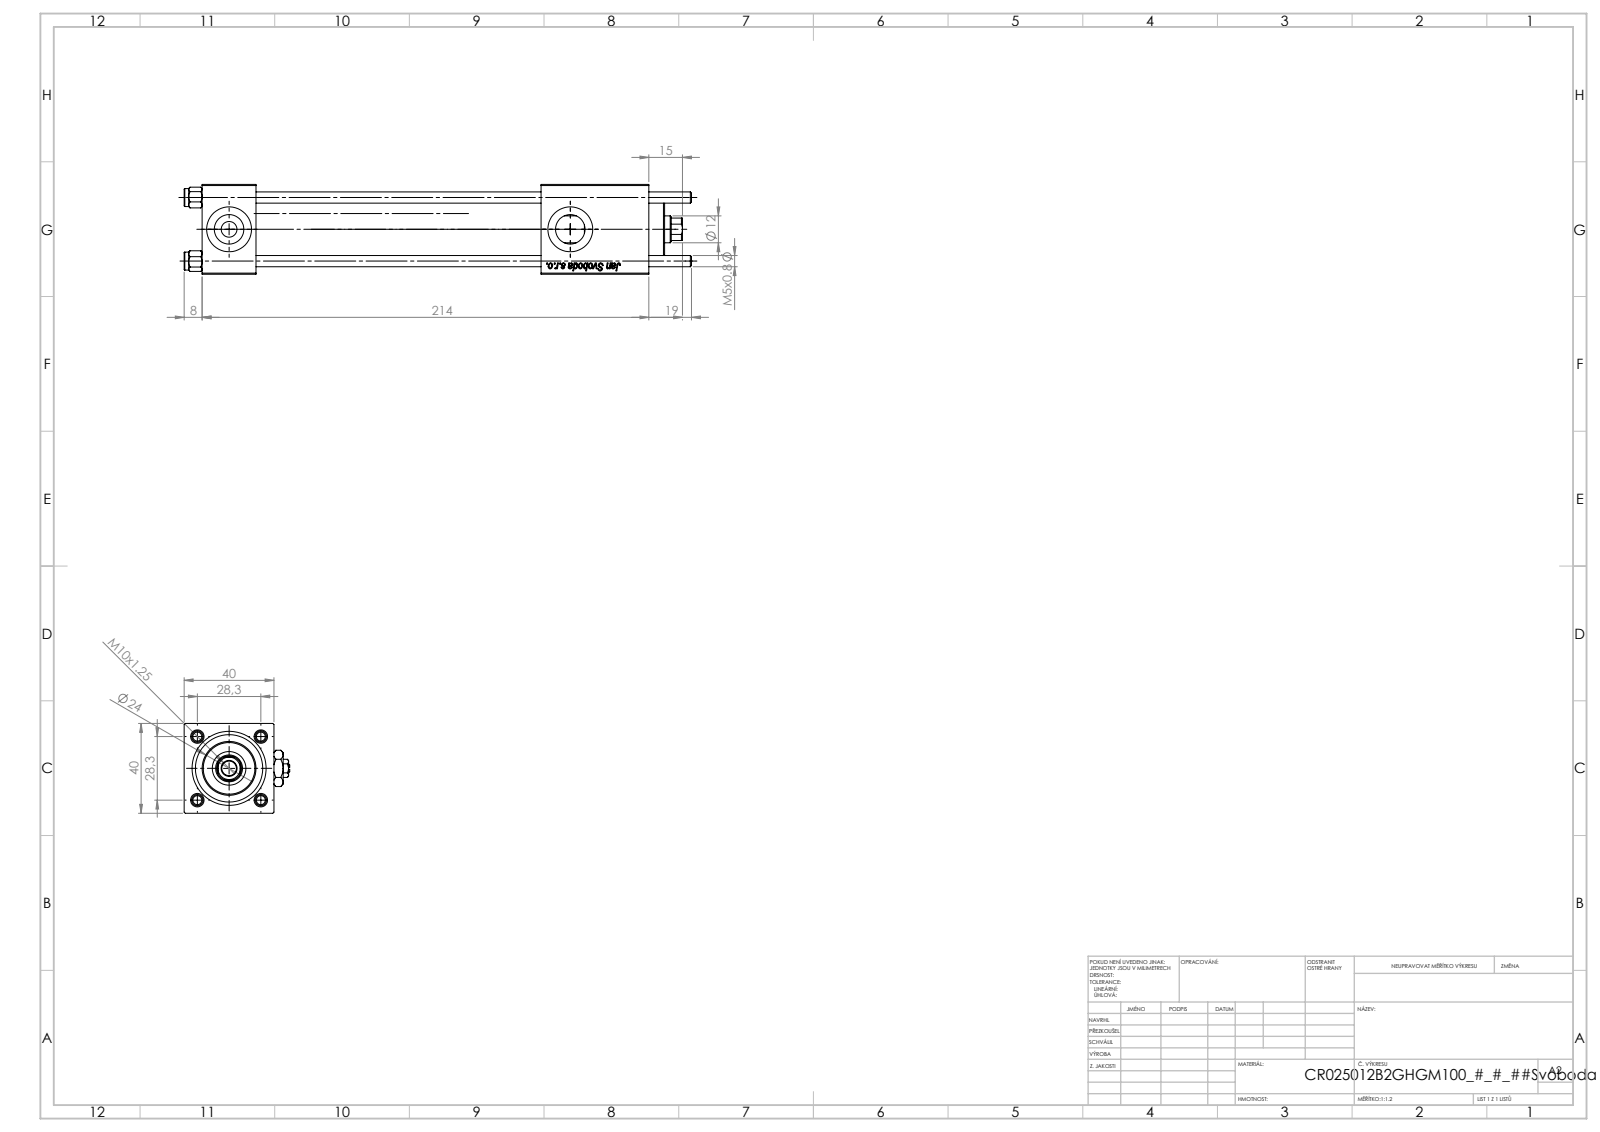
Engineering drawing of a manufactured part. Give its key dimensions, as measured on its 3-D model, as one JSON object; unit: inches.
{"part_name": "V215CR_VCP_B; V215CR_B-1; NUT_M5_B; Zatka_pro_OIL_PORT (+2 more)", "step_written_by": "SolidWorks 2019 (CONFIG_CONTROL_DESIGN)", "units": "inches", "bodies": {"solids": 12, "faces": 1208, "planar": 452, "cylindrical": 86, "other": 670}, "overall_size": [8.898, 1.85, 1.575], "volume_in3": 11.02, "surface_area_in2": 126.7, "round_holes": [[0.197, 4], [0.787, 3], [0.276, 2], [0.518, 2], [0.256, 1], [0.472, 1], [0.591, 1], [0.984, 1], [1.181, 1]], "round_bosses_or_shafts": [[0.315, 4], [1.22, 1], [0.945, 1]], "partial_cylinders_radius": [[0.217, 1]], "face_to_face_distances": [1.575, 0.945, 6.705, 5.76, 7.835, 5.945, 5, 0.76, 6.89, 1.89], "hole_center_spacings": [0.788, 1.114, 1.576, 5.984]}
